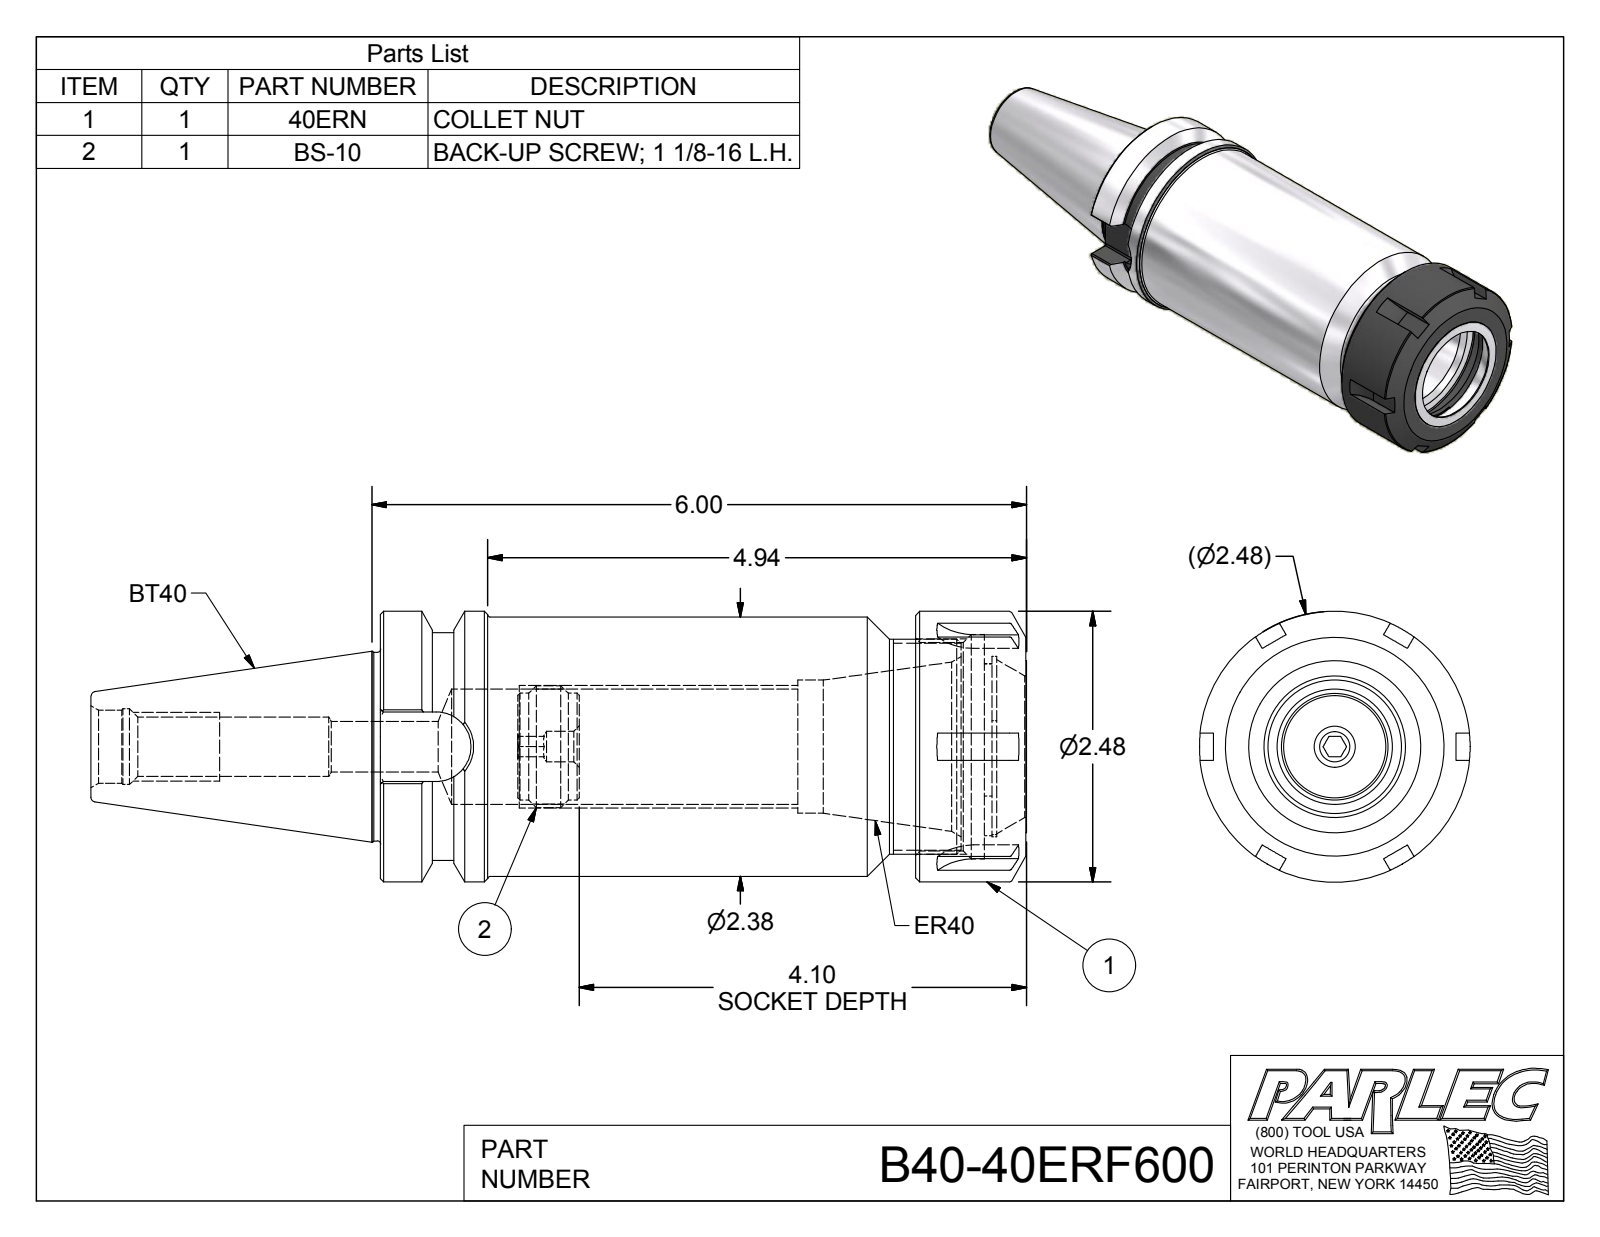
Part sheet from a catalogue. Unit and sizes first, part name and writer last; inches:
Units: inches
Overall size (bounding box): 8.575 × 2.48 × 2.48
Round holes (diameter × count): ⌀0.22 ×1, ⌀0.28 ×1, ⌀0.466 ×1, ⌀0.545 ×1, ⌀0.67 ×1, ⌀0.694 ×1, ⌀1.057 ×1, ⌀1.22 ×1, ⌀1.3 ×1, ⌀1.618 ×1, ⌀1.909 ×1, ⌀2.057 ×1
Round bosses / shafts (diameter × count): ⌀2.48 ×1, ⌀2.48 ×1, ⌀2.375 ×1, ⌀2.087 ×1, ⌀1.969 ×1, ⌀1.73 ×1, ⌀1.118 ×1, ⌀0.98 ×1
Partial cylindrical surfaces — rounded edges, fillets, slot ends (radius × count): R0.02 ×20, R0.319 ×1, R0.728 ×1, R0.827 ×1
Main face-to-face distances: 5.922, 4.897, 1.025, 5.532, 0.635, 0.39, 5.322, 0.425, 0.21, 0.6
Hole centre spacings: 0.09
Volume: 23.2 in³ · Surface area: 104.7 in²
Bodies: 3 solids, 176 faces (67 planar, 48 cylindrical, 61 other)
Part name (STEP PRODUCT): B40-40ER6-1; 40ERN; BS-10; B40-40ERF600
STEP written by: Autodesk Inventor 2016 (AUTOMOTIVE_DESIGN)
